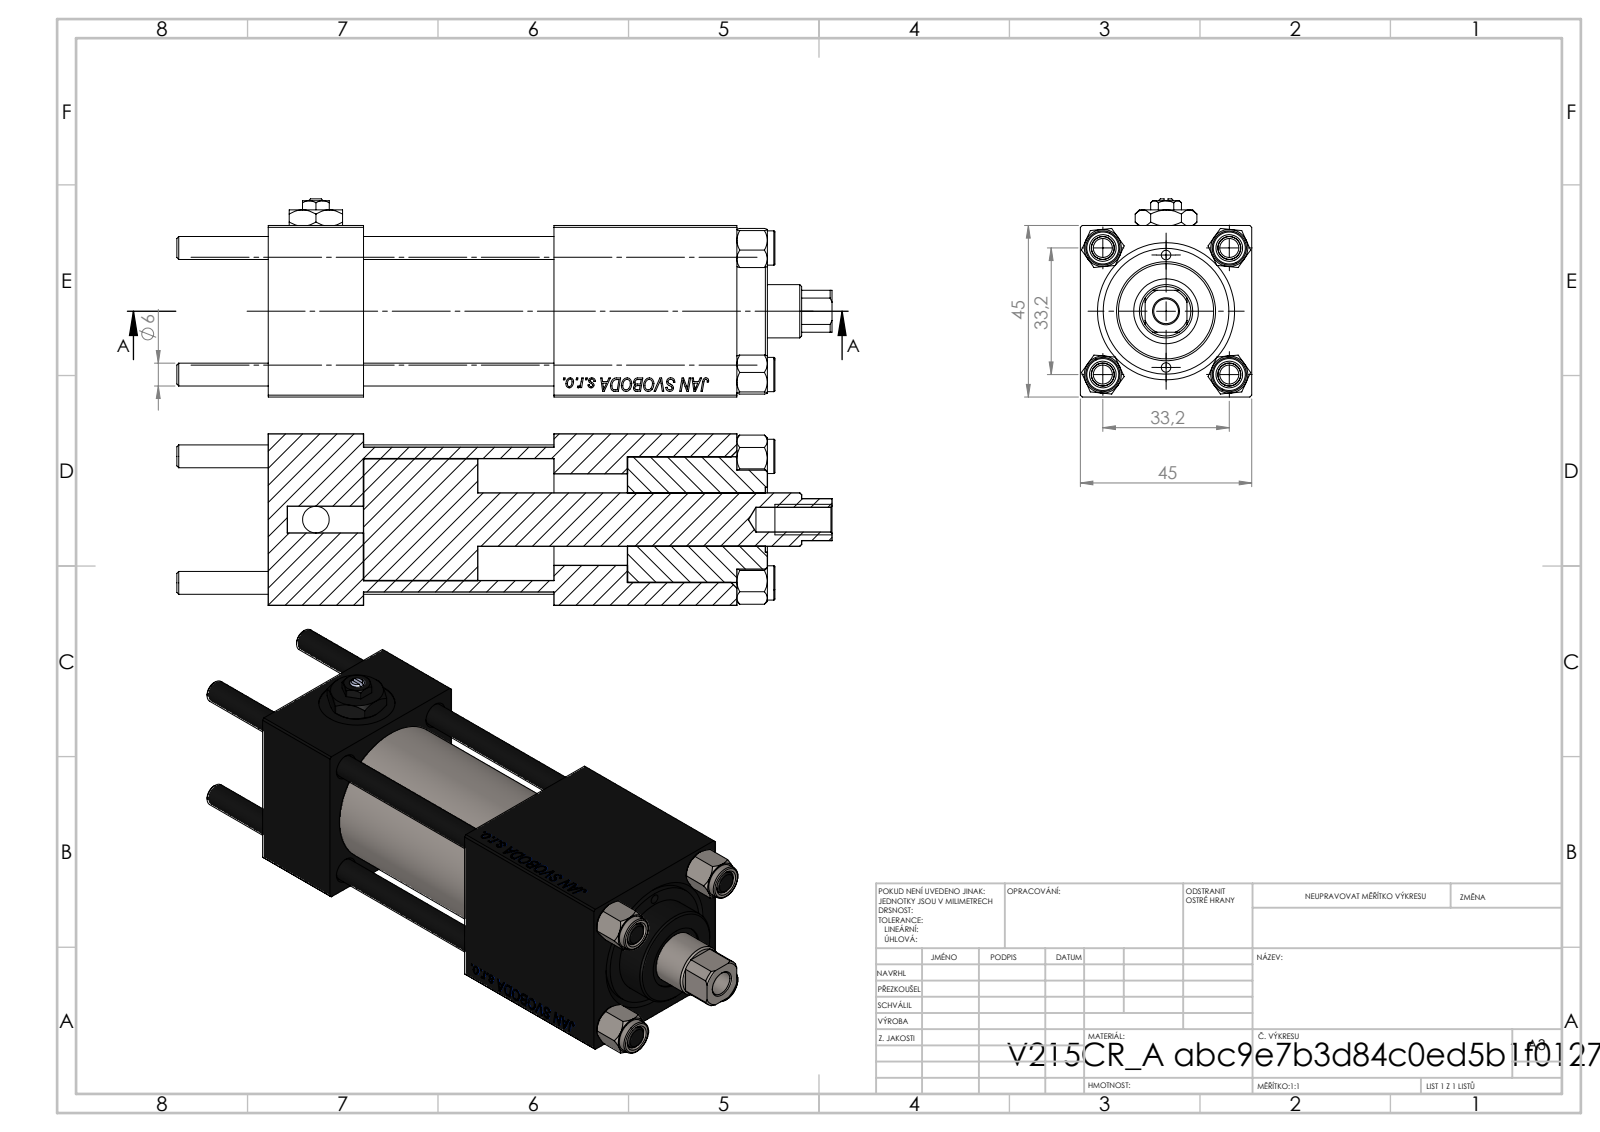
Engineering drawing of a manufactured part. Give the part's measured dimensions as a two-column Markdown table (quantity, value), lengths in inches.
| quantity | value |
| --- | --- |
| part name | CR025_012_A_0_G_A_G_M_020_+#_##_TYCINKA; NUT_M5; V215CR_BODY_A; V215CR_VCP (+2 more) |
| STEP written by | SolidWorks 2019 (CONFIG_CONTROL_DESIGN) |
| units | inches |
| bodies | 12 solids, 1190 faces (544 planar, 88 cylindrical, 558 other) |
| overall size | 6.772 × 2.047 × 1.772 |
| volume | 12.05 in³ |
| surface area | 114.7 in² |
| round holes (diameter × count) | 0.236 × 4, 0.098 × 2, 0.276 × 2, 0.518 × 2, 0.787 × 2, 0.256 × 1, 0.551 × 1, 0.669 × 1, 0.945 × 1, 1.26 × 1, 1.299 × 1 |
| round bosses / shafts (diameter × count) | 0.354 × 4, 1.496 × 1, 1.024 × 1 |
| partial cylindrical surfaces (radius × count) | 0.256 × 1 |
| main face-to-face distances | 1.772, 0.984, 4.843, 3.858, 1.969, 2.953, 1.89, 3.713, 2.728, 0.76 |
| hole center spacings | 0.657, 0.924, 1.307, 1.396, 0.581, 1.848, 1.161, 2.972 |
